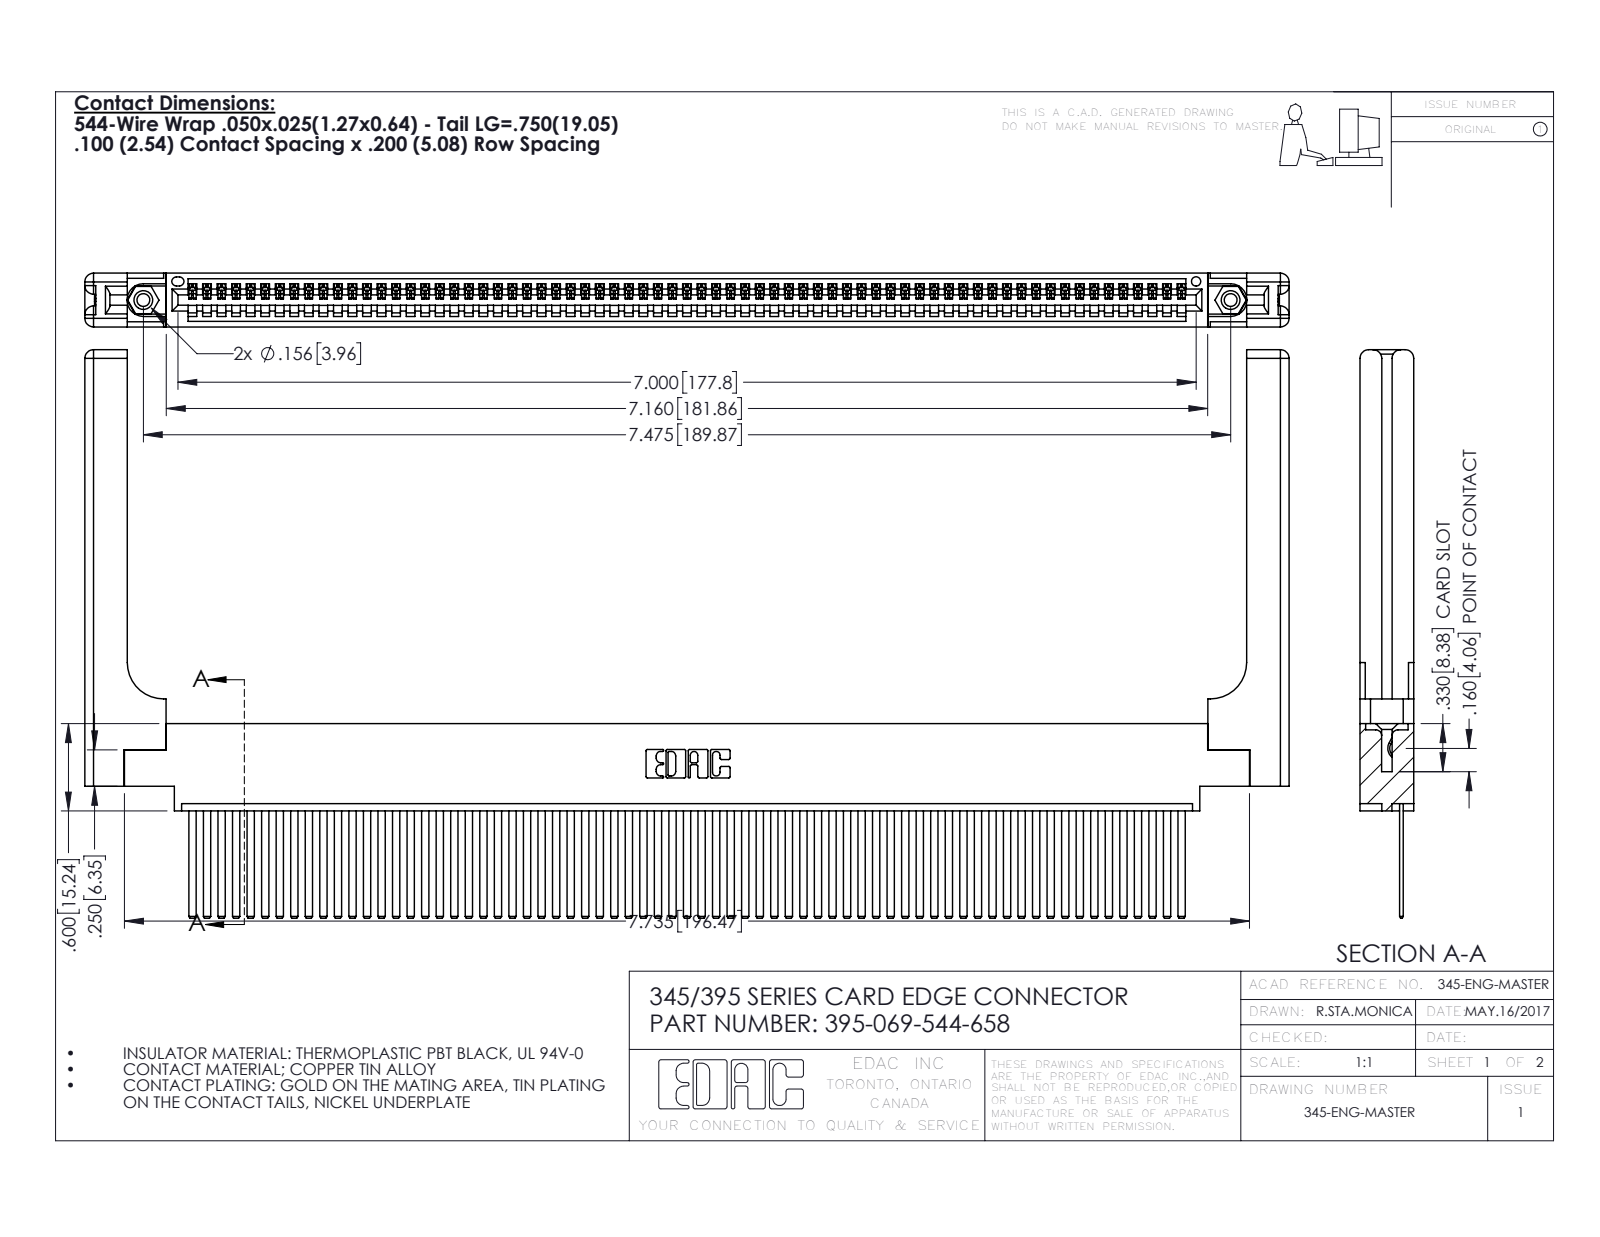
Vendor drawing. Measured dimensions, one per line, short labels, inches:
name: 345-292-001_345-293-144; 345 Part_0.170 Offset - 0.156 Dia-TH; 395-069-544-658; 345-220-058_345-220-058 (+1 more)
written by: SolidWorks 2016 (CONFIG_CONTROL_DESIGN)
unit: in
bodies: 74 solids, 3974 faces (2716 planar, 1198 cylindrical, 60 other)
size: 8.279 × 3.907 × 0.37
volume: 1.793 in³; area: 55.72 in²
holes: 2× ⌀0.089, 2× ⌀0.125, 2× ⌀0.156, 1× ⌀0.064
bosses: 2× ⌀0.155
rounds: 138× R0.006, 22× R0.01, 16× R0.06, 6× R0.007, 6× R0.031, 3× R0.026, 2× R0.03, 2× R0.031
face distances: 0.072, 0.298, 0.37, 0.098, 0.272, 0.025, 0.2, 0.225, 0.148, 0.15
hole spacings: 0.27, 7.239, 7.475
